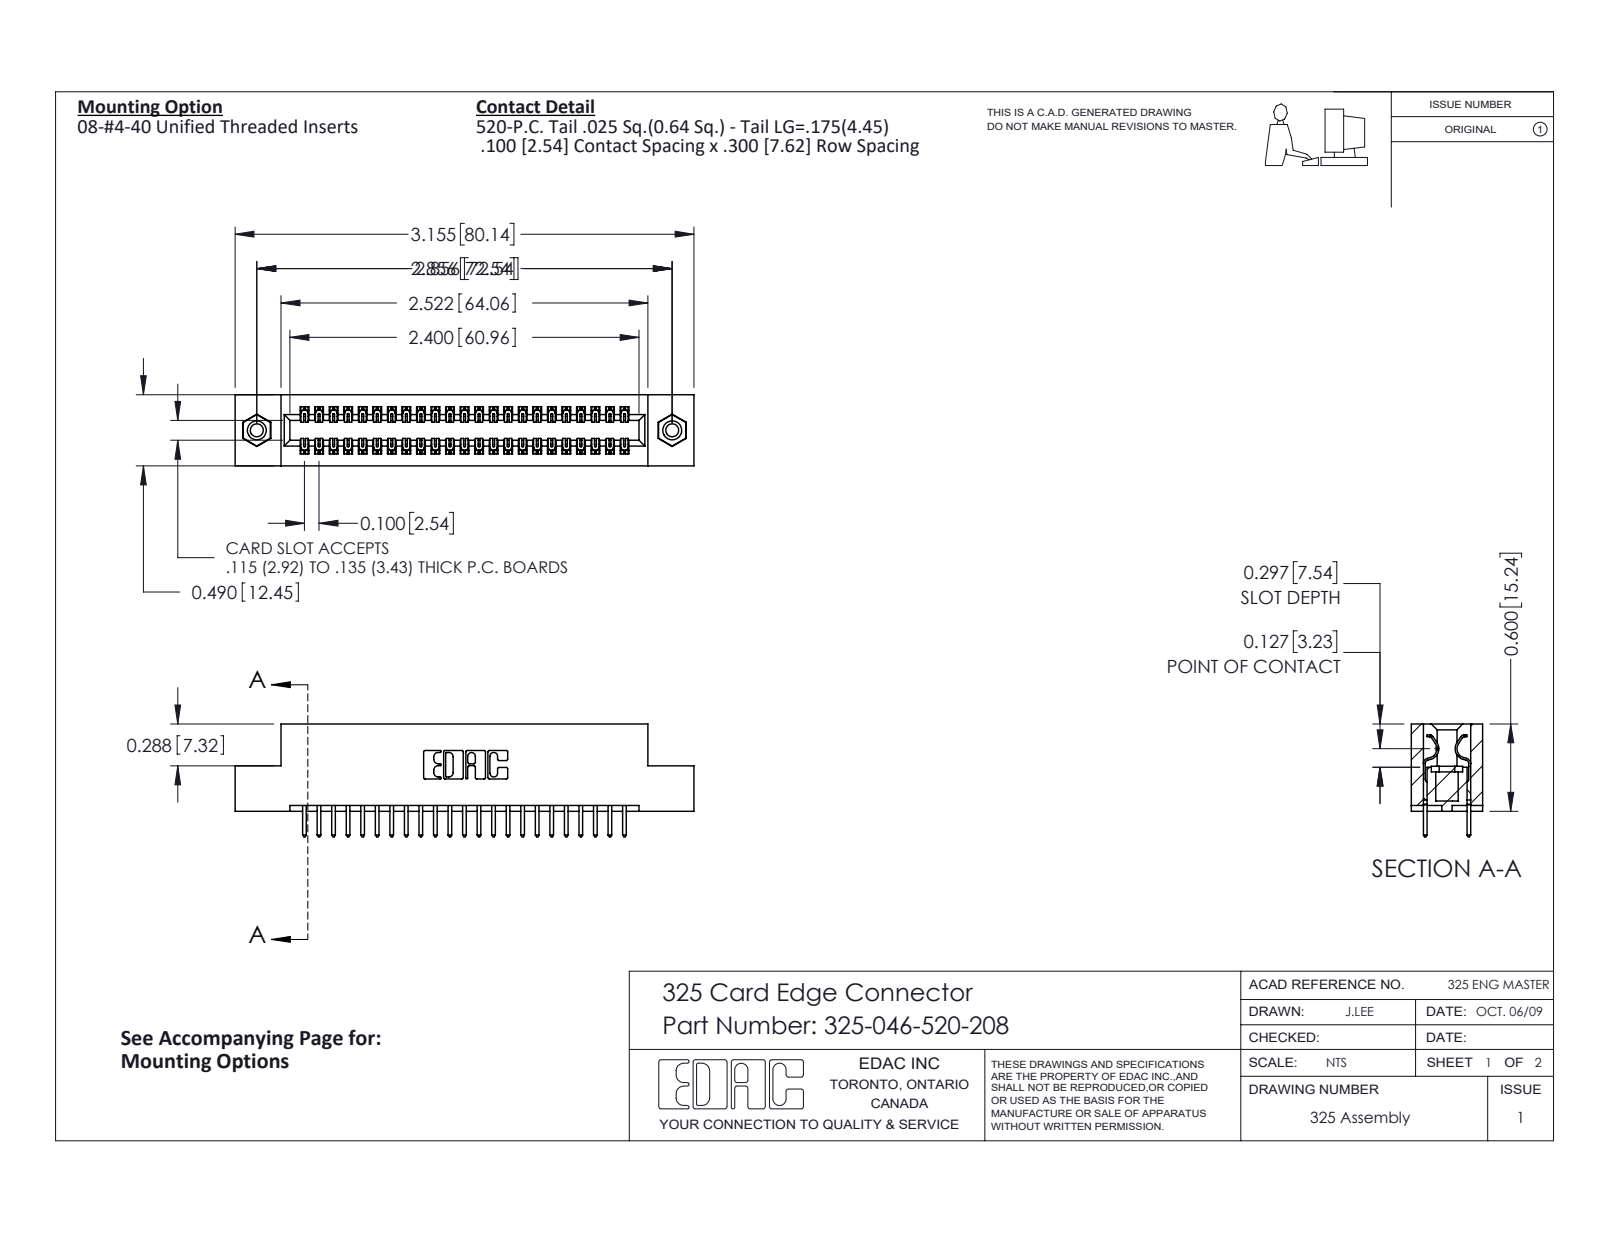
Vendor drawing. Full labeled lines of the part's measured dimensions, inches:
Part name (STEP PRODUCT): 325-292-001_325-293-120; 325-046-520-208; 345-250-001_345-250-003-102; 325 Part_TI
STEP written by: SolidWorks 2016 (CONFIG_CONTROL_DESIGN)
Units: inches
Bodies: 49 solids, 2566 faces (1758 planar, 792 cylindrical, 16 other)
Overall size (bounding box): 3.155 × 0.775 × 0.49
Volume: 0.62 in³ · Surface area: 18.24 in²
Round holes (diameter × count): ⌀0.089 ×2, ⌀0.125 ×2, ⌀0.16 ×2
Round bosses / shafts (diameter × count): ⌀0.155 ×2
Partial cylindrical surfaces — rounded edges, fillets, slot ends (radius × count): R0.006 ×69, R0.01 ×46, R0.01 ×22, R0.007 ×6, R0.031 ×6, R0.026 ×3, R0.014 ×2, R0.022 ×2
Main face-to-face distances: 0.083, 0.407, 0.3, 0.49, 0.107, 0.383, 0.025, 0.325, 0.04, 0.6
Hole centre spacings: 2.856
